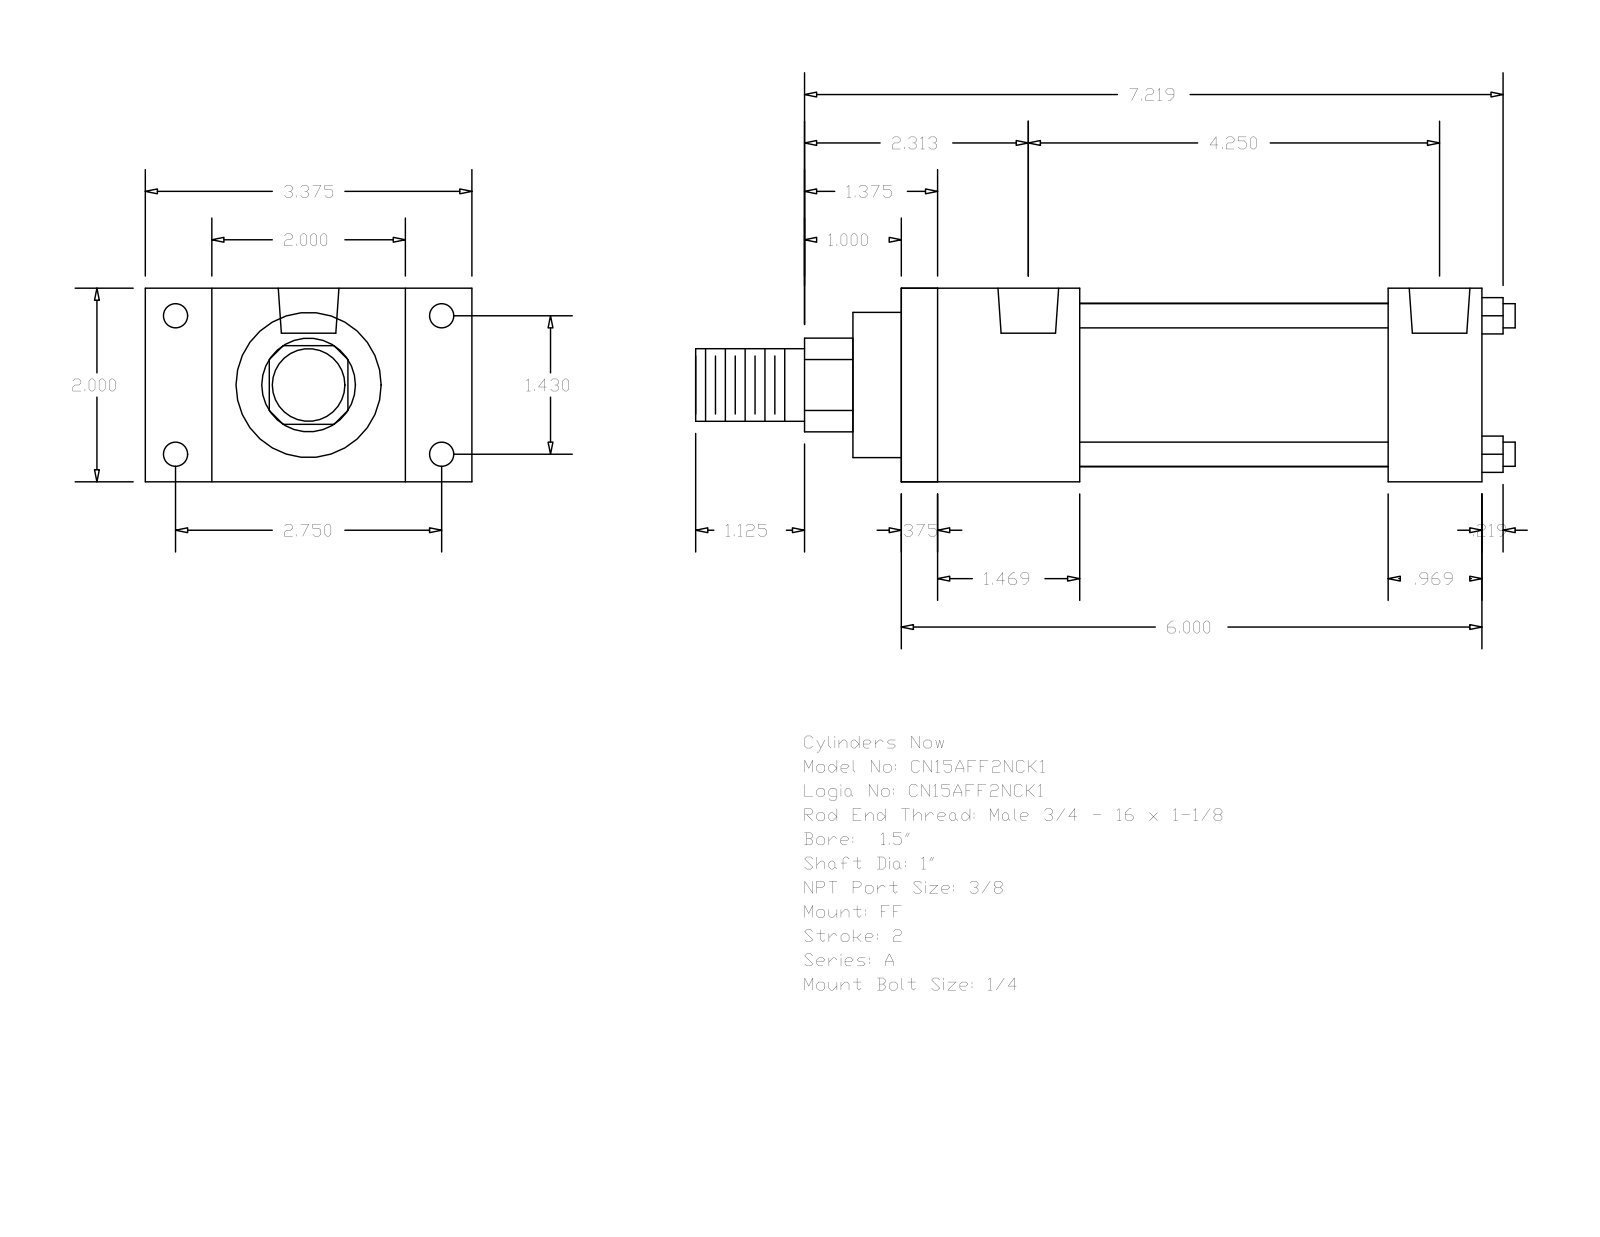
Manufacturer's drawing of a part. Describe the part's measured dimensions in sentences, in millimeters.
The part is named "A_FF__0150_1". Its 3-D file was written by "GSSL Pune (CONFIG_CONTROL_DESIGN)". It is 0 solids with 92 faces: 64 planar, 28 cylindrical and 0 other. Overall it measures 215.11 by 85.72 by 50.8 millimeters. Round holes: 4 of diameter 5.56, 4 of diameter 6.35, 2 of diameter 15.93. Round bosses or shafts: 4 of diameter 6.35, 1 of diameter 42.93, 1 of diameter 38.1, 1 of diameter 25.4, 1 of diameter 19.05. Partial cylindrical surfaces (rounded edges, fillets, slot ends): 1 of radius 12.29. The main face-to-face distances are 50.8, 152.4, 9.52, 142.88, 46.83, 127.79, 37.31, 118.27, 80.96, 105.57. The hole center spacings are 3.97, 36.32, 69.84, 78.72, 100.01, 103.98, 107.95.
